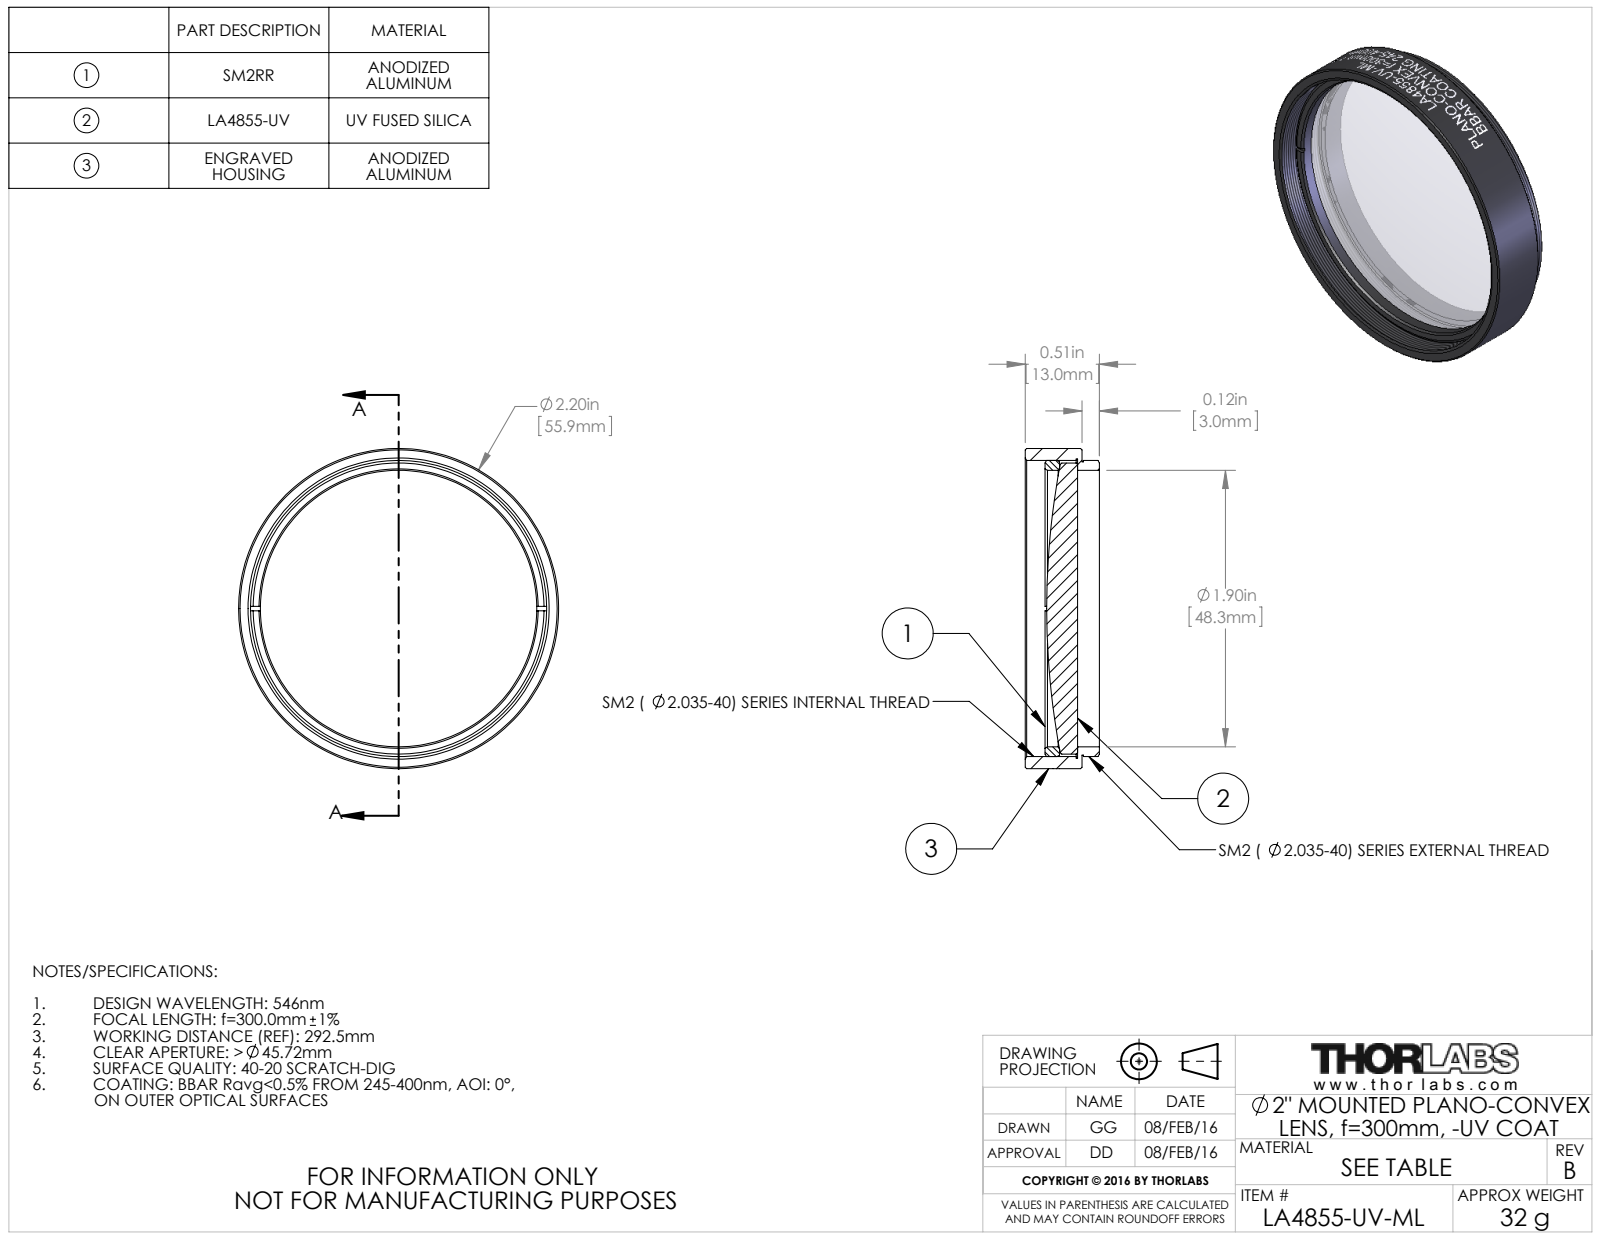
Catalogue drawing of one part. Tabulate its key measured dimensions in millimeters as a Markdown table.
| quantity | value |
| --- | --- |
| part name | TTN039407-E0W |
| STEP written by | SolidWorks 2014 (CONFIG_CONTROL_DESIGN) |
| units | millimeters |
| bodies | 3 solids, 149 faces (16 planar, 109 cylindrical, 24 other) |
| overall size | 55.88 × 55.88 × 12.95 |
| volume | 13 625 mm³ |
| surface area | 11 325 mm² |
| round holes (diameter × count) | 48.26 × 1, 52.2 × 1 |
| round bosses / shafts (diameter × count) | 55.88 × 1, 51.69 × 1, 51.18 × 1, 50.8 × 1 |
| main face-to-face distances | 0.76, 9.91, 9.15, 3.05, 3.81, 12.96, 6.97, 3.92, 3.16, 5.99 |
